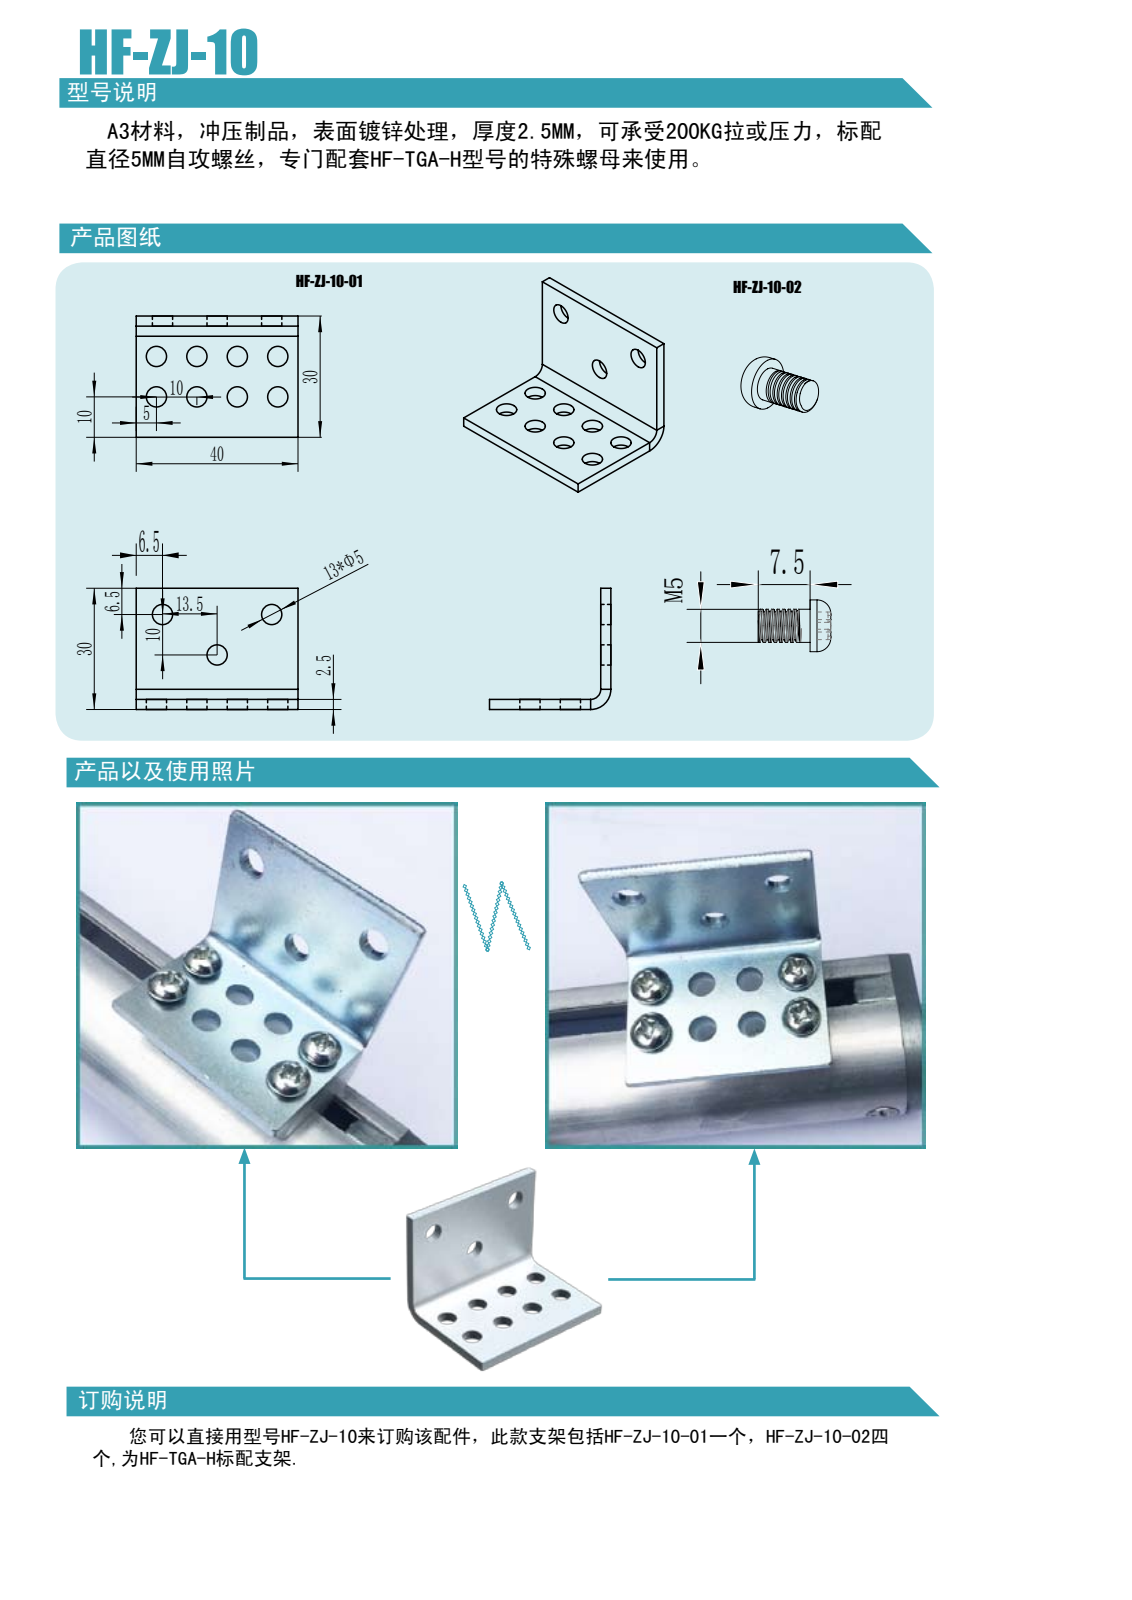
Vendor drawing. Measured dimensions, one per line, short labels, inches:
name: ZJ-10
written by: PRO/ENGINEER BY PARAMETRIC TECHNOLOGY CORPORATION, 2008380 (CONFIG_CONTROL_DESIGN)
unit: in
bodies: 1 solid, 36 faces (12 planar, 24 cylindrical, 0 other)
size: 40 × 30 × 30
volume: 5 049 in³; area: 4 951 in²
holes: 11× ⌀5
rounds: 1× R2.5, 1× R5
face distances: 2.5, 30, 27.5, 40
hole spacings: 10, 14.142, 20, 22.361, 16.8, 30, 31.623, 27
